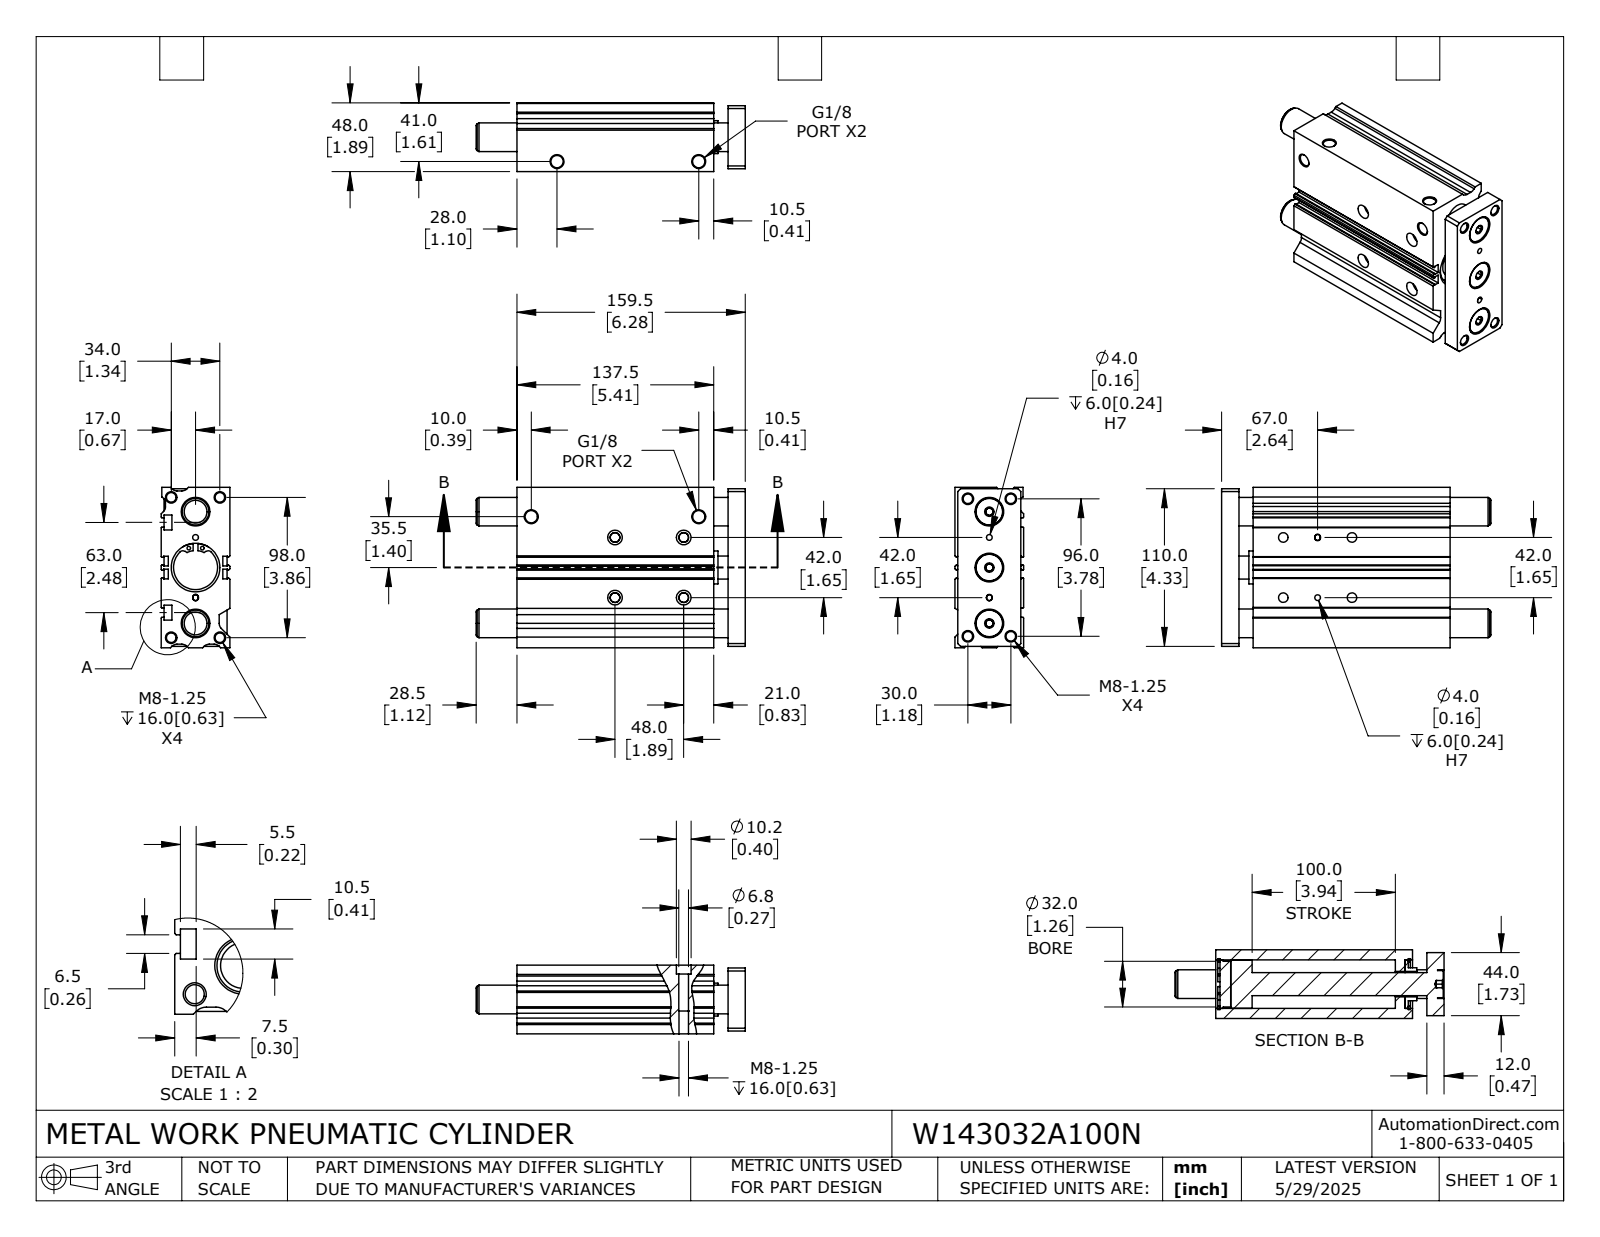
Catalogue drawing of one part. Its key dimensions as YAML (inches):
part_name: "W143032A100N_ROD; W143032A100N_BODY; W143032A100N"
step_written_by: "SolidWorks 2024 (CONFIG_CONTROL_DESIGN)"
units: inches
bodies: {solids: 6, faces: 394, planar: 195, cylindrical: 149, other: 50}
overall_size: [7.402, 4.409, 1.89]
volume: 40.74
surface_area: 246
round_holes:
  - {diameter: 0.262, count: 12}
  - {diameter: 0.098, count: 4}
  - {diameter: 0.157, count: 4}
  - {diameter: 0.268, count: 4}
  - {diameter: 0.337, count: 4}
  - {diameter: 0.402, count: 4}
  - {diameter: 0.197, count: 3}
  - {diameter: 0.787, count: 3}
  - {diameter: 0.697, count: 1}
  - {diameter: 1.211, count: 1}
round_bosses_or_shafts:
  - {diameter: 0.748, count: 3}
  - {diameter: 1.406, count: 2}
  - {diameter: 1.339, count: 1}
  - {diameter: 1.26, count: 1}
  - {diameter: 0.906, count: 1}
  - {diameter: 0.63, count: 1}
partial_cylinders:
  - {radius: 0.197, count: 9}
  - {radius: 0.079, count: 4}
  - {radius: 0.118, count: 4}
  - {radius: 0.507, count: 2}
face_to_face_distances: [1.89, 0.118, 0.295, 0.098, 0.079, 0.472, 1.693, 0.866, 4.409, 0.197]
hole_center_spacings: [0.088, 0.348, 0.566, 0.689, 0.776, 0.945, 1.019, 1.216]
